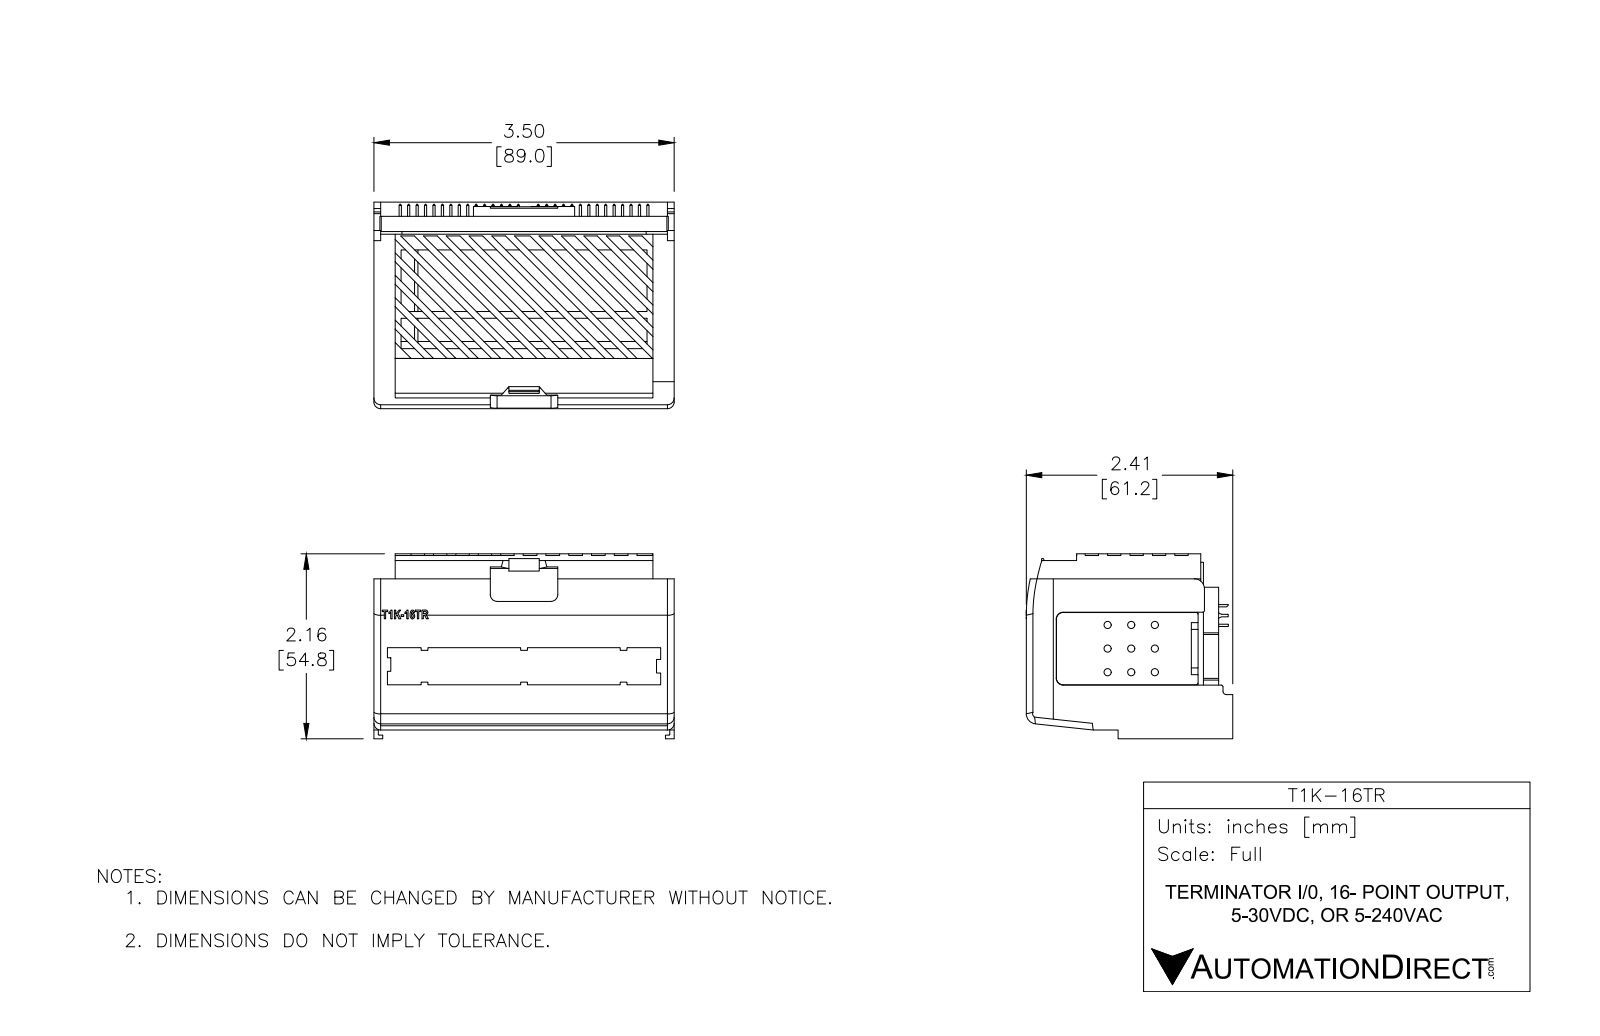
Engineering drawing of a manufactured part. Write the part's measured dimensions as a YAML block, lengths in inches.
part_name: "T1K-16TR"
step_written_by: "SolidWorks 2013 (AUTOMOTIVE_DESIGN)"
units: inches
bodies: {solids: 1, faces: 634, planar: 439, cylindrical: 181, other: 14}
overall_size: [3.492, 2.563, 2.416]
volume: 2.774
surface_area: 84.51
round_holes:
  - {diameter: 0.118, count: 16}
round_bosses_or_shafts:
  - {diameter: 0.028, count: 56}
partial_cylinders:
  - {radius: 0.138, count: 18}
  - {radius: 0.039, count: 5}
  - {radius: 0.01, count: 3}
  - {radius: 0.022, count: 3}
  - {radius: 0.059, count: 2}
  - {radius: 0.315, count: 1}
  - {radius: 0.394, count: 1}
  - {radius: 0.709, count: 1}
face_to_face_distances: [0.079, 3.413, 2.179, 0.02, 2.354, 3.492, 0.059, 2.176, 2.1, 3.335]
hole_center_spacings: [0.203, 0.406, 0.608, 0.811, 1.014, 1.217, 1.419, 1.622]
